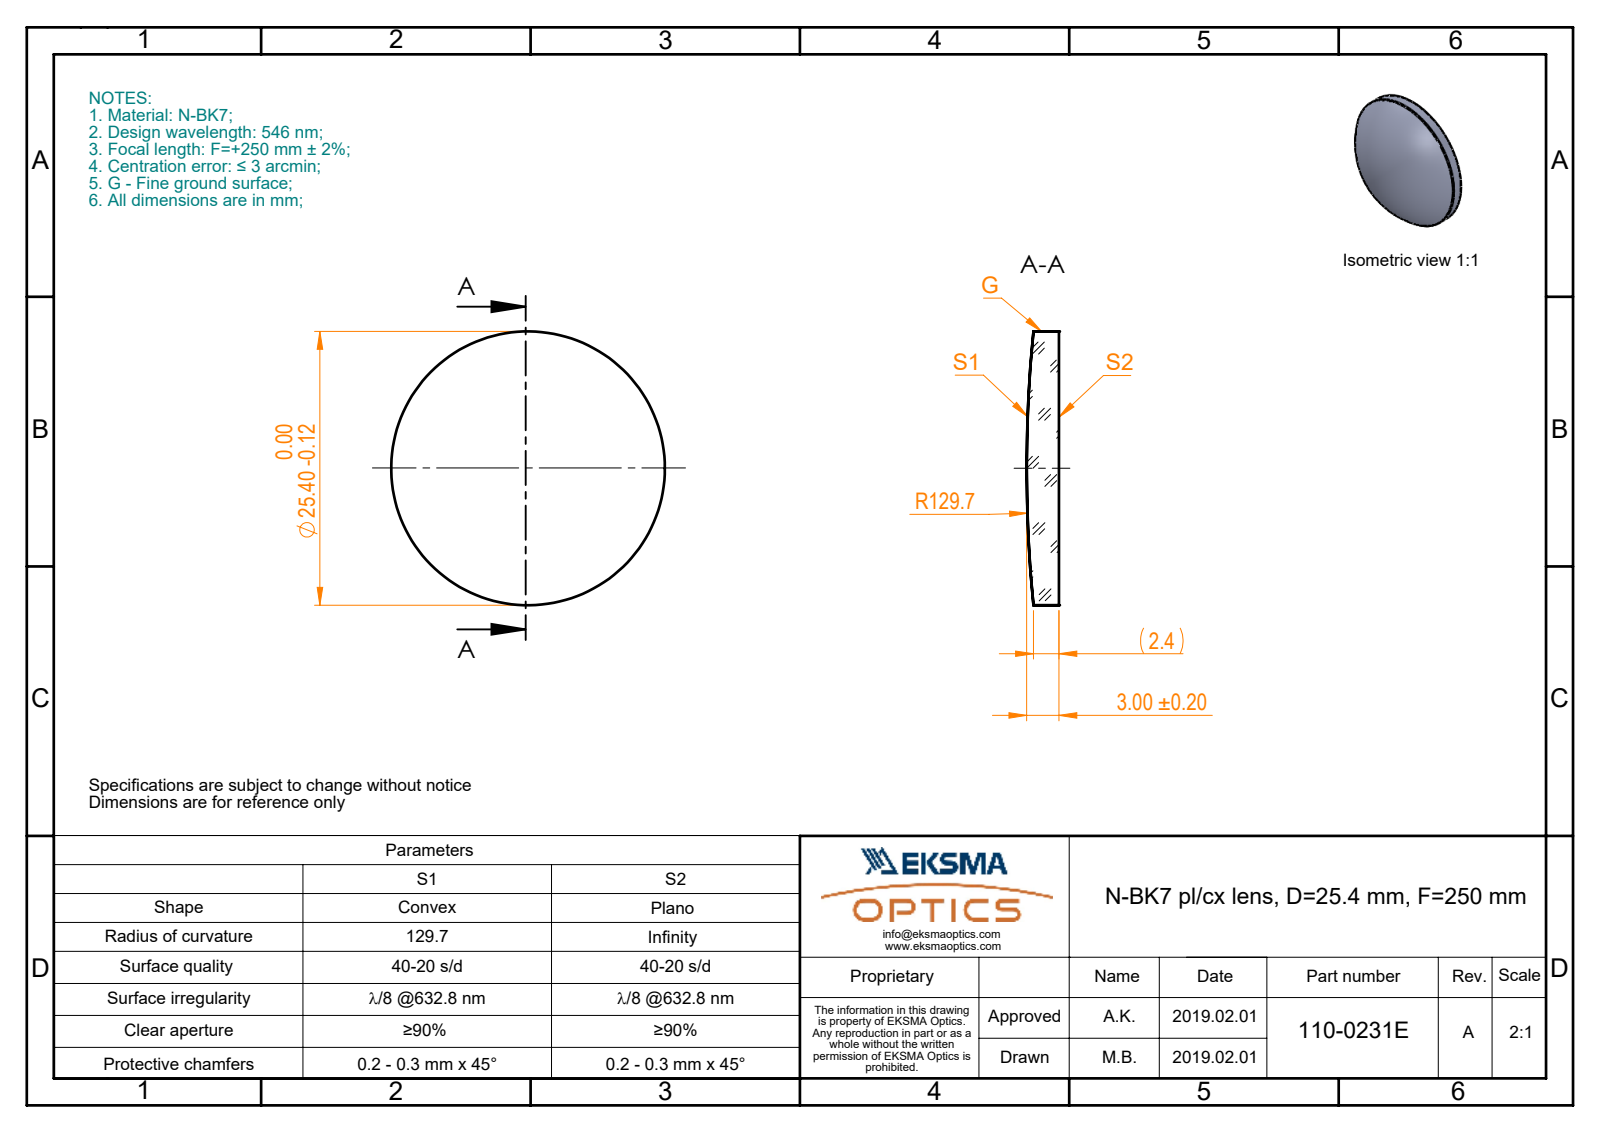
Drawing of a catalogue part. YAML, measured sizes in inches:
part_name: "110-0235E BK7 pl-cx 25.4 F250"
step_written_by: "SolidWorks 2017 (CONFIG_CONTROL_DESIGN)"
units: inches
bodies: {solids: 1, faces: 5, planar: 1, cylindrical: 2, other: 2}
overall_size: [1, 1, 0.118]
volume: 0.083
surface_area: 1.866
round_bosses_or_shafts:
  - {diameter: 1, count: 1}
